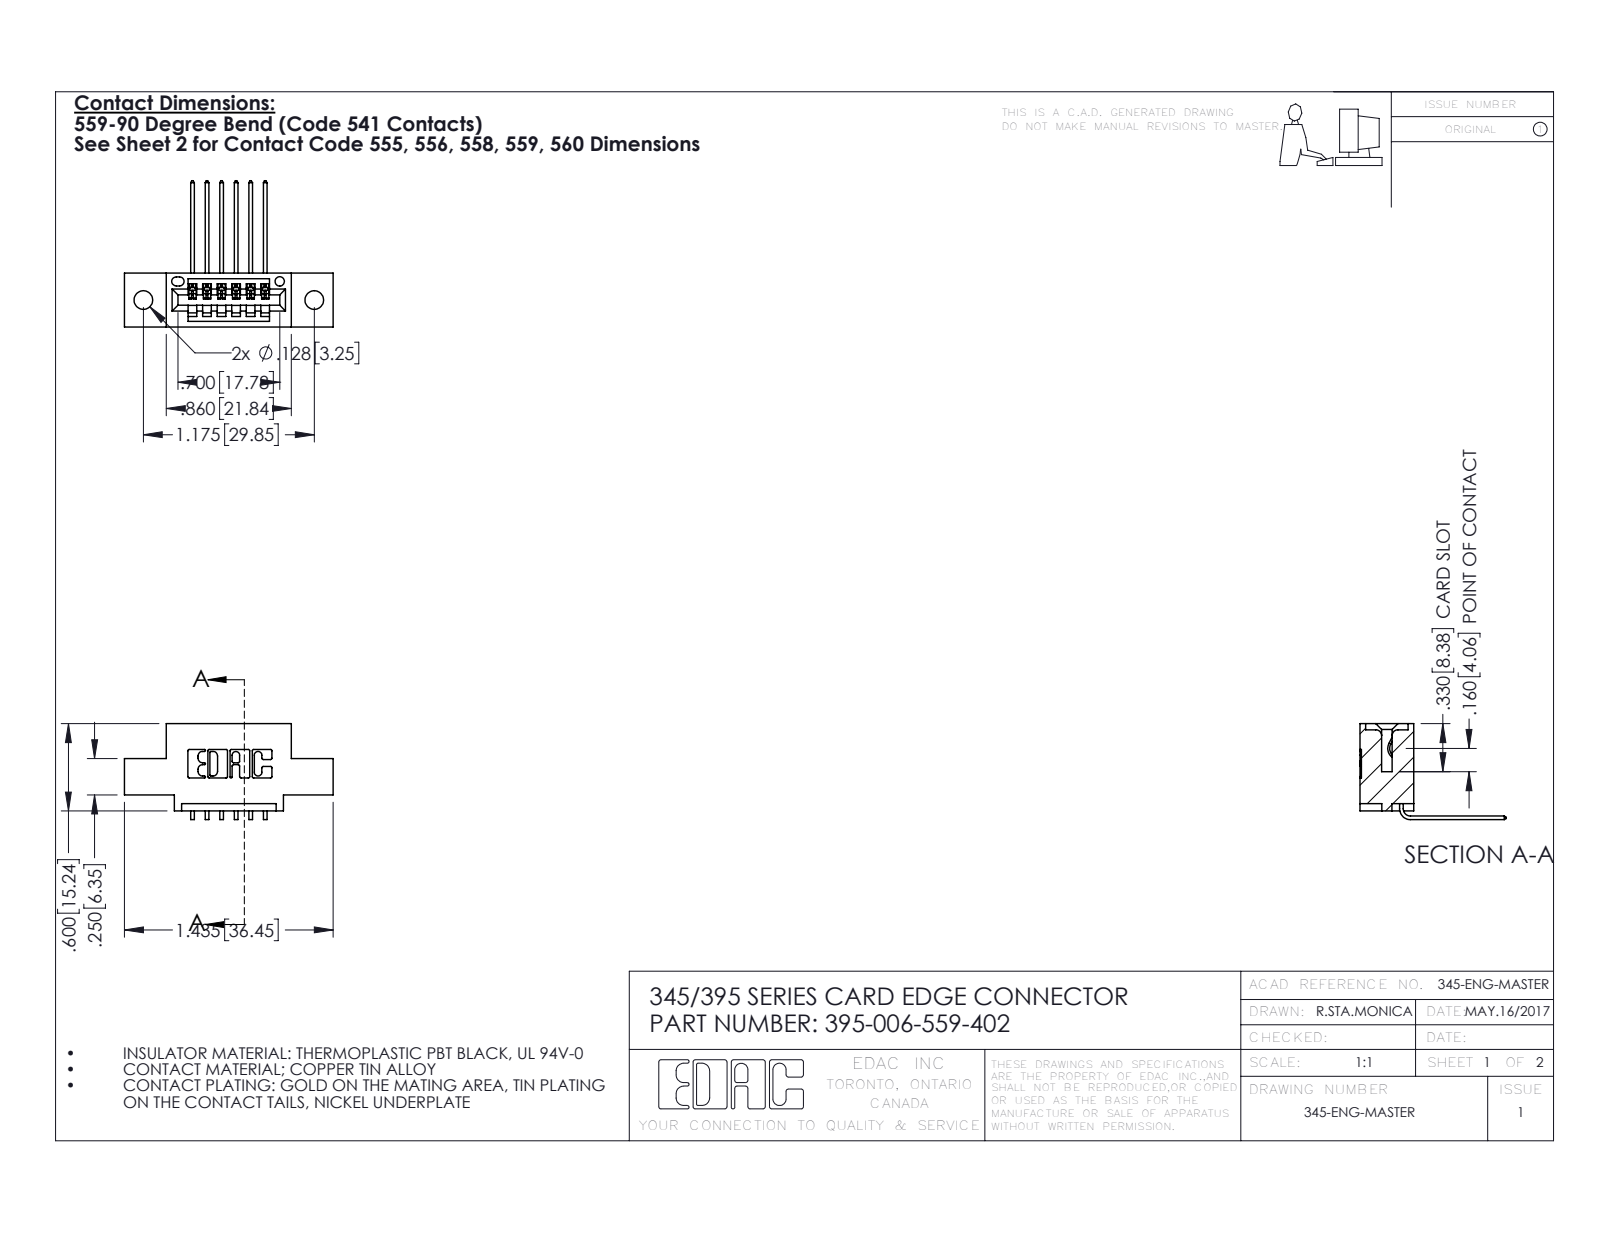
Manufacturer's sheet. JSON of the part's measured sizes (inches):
{"part_name": "395-006-559-402; 345 Part_0.110 Offset - 0.128 Dia; 345-292-001_558 559 Tail - 1", "step_written_by": "SolidWorks 2016 (CONFIG_CONTROL_DESIGN)", "units": "inches", "bodies": {"solids": 7, "faces": 490, "planar": 336, "cylindrical": 154, "other": 0}, "overall_size": [1.435, 1.005, 0.659], "volume_in3": 0.188, "surface_area_in2": 5.468, "round_holes": [[0.128, 2], [0.064, 1]], "partial_cylinders_radius": [[0.01, 22], [0.006, 12], [0.007, 6], [0.031, 6], [0.026, 3], [0.031, 2], [0.04, 2], [0.014, 1]], "face_to_face_distances": [0.2, 0.37, 0.1, 0.072, 0.298, 0.16, 0.025, 0.06, 0.3, 0.25], "hole_center_spacings": [0.27, 0.946, 1.175]}
